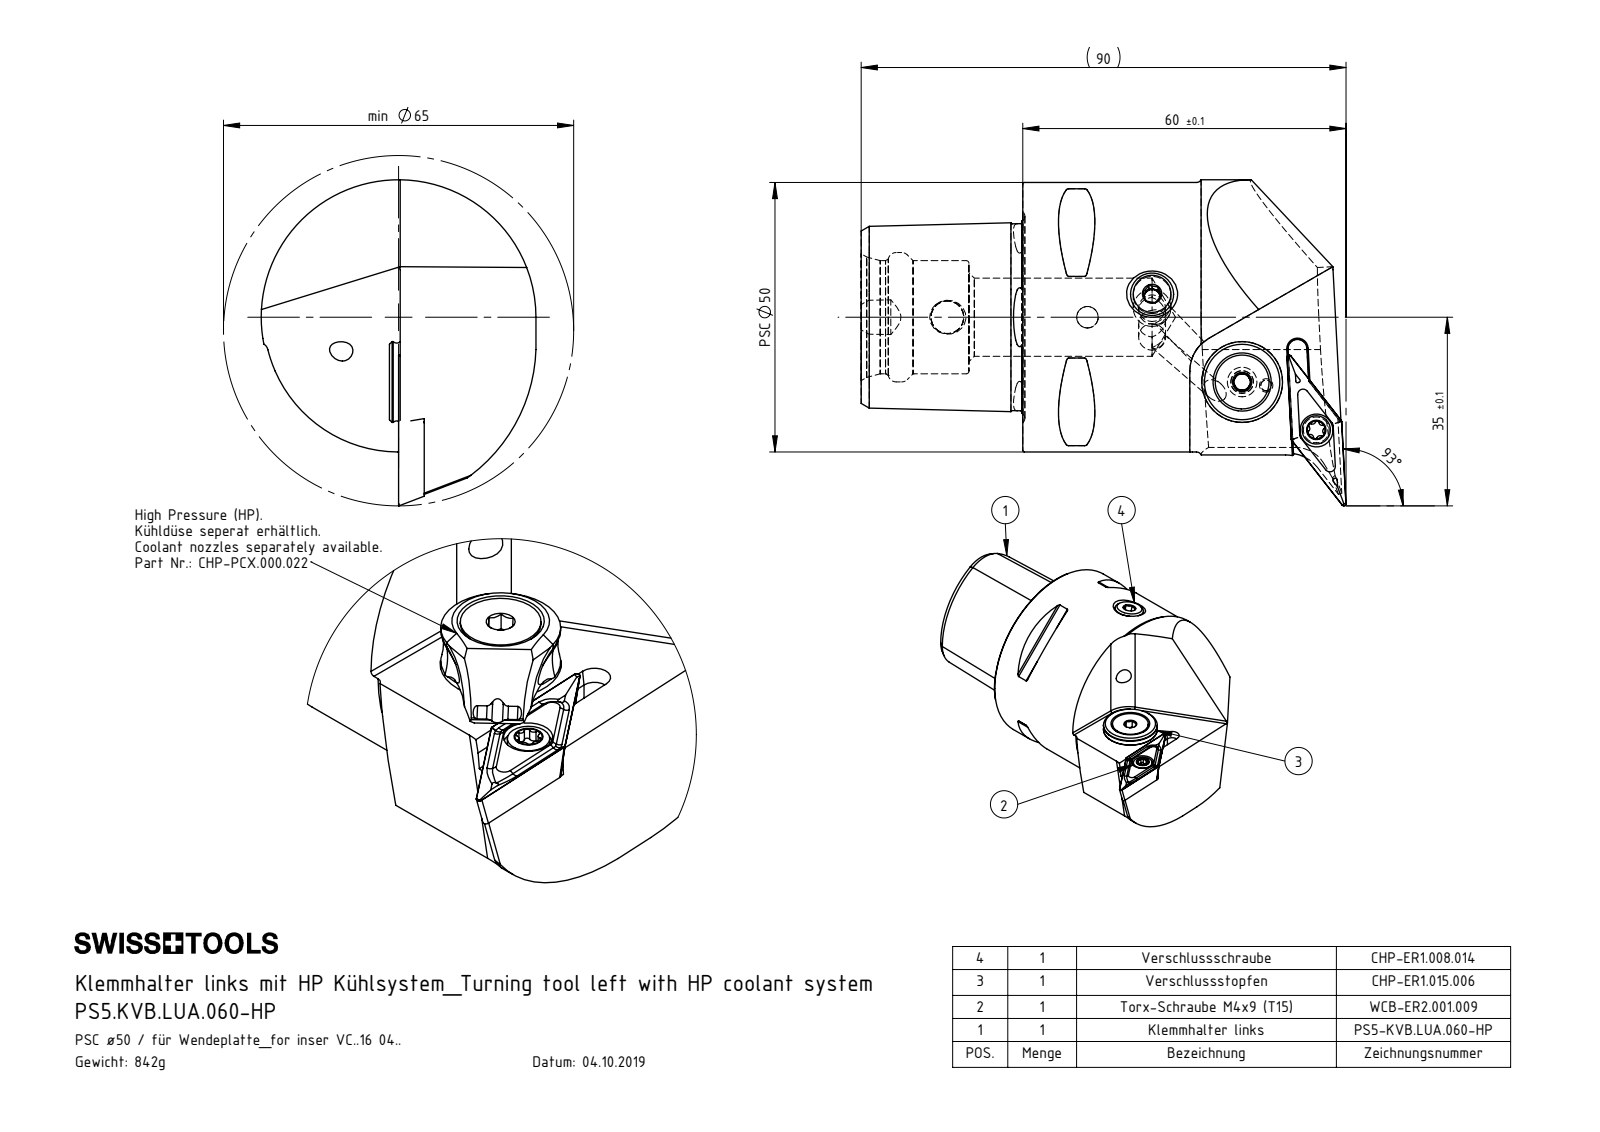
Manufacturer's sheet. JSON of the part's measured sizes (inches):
{"part_name": "PS5.KVB.LUA.060-HP; PS5-KVB.LUA.060-HP_B; CHP-ER1.008.014_A; VCMT160404 (+6 more)", "step_written_by": "SolidWorks 2017 (AUTOMOTIVE_DESIGN)", "units": "inches", "bodies": {"solids": 8, "faces": 277, "planar": 93, "cylindrical": 62, "other": 122}, "overall_size": [3.543, 2.382, 2.008], "volume_in3": 6.54, "surface_area_in2": 35.59, "round_holes": [[0.13, 2], [0.165, 2], [0.24, 2], [0.047, 1], [0.079, 1], [0.098, 1], [0.118, 1], [0.157, 1], [0.173, 1], [0.197, 1], [0.205, 1], [0.276, 1]], "round_bosses_or_shafts": [[1.969, 1], [0.591, 1], [0.528, 1], [0.394, 1], [0.315, 1], [0.217, 1], [0.207, 1], [0.197, 1]], "partial_cylinders_radius": [[0.02, 10], [0.013, 6], [0.023, 6], [0.276, 2], [0.069, 1], [0.157, 1], [1.004, 1], [1.201, 1]], "face_to_face_distances": [1.181, 0.177, 2.402, 1.22, 0.176, 0.755, 1.748, 0.815, 0.817, 0.992], "hole_center_spacings": [0.177, 0.49, 0.494, 0.645, 0.648, 1.024, 1.226, 1.398]}
